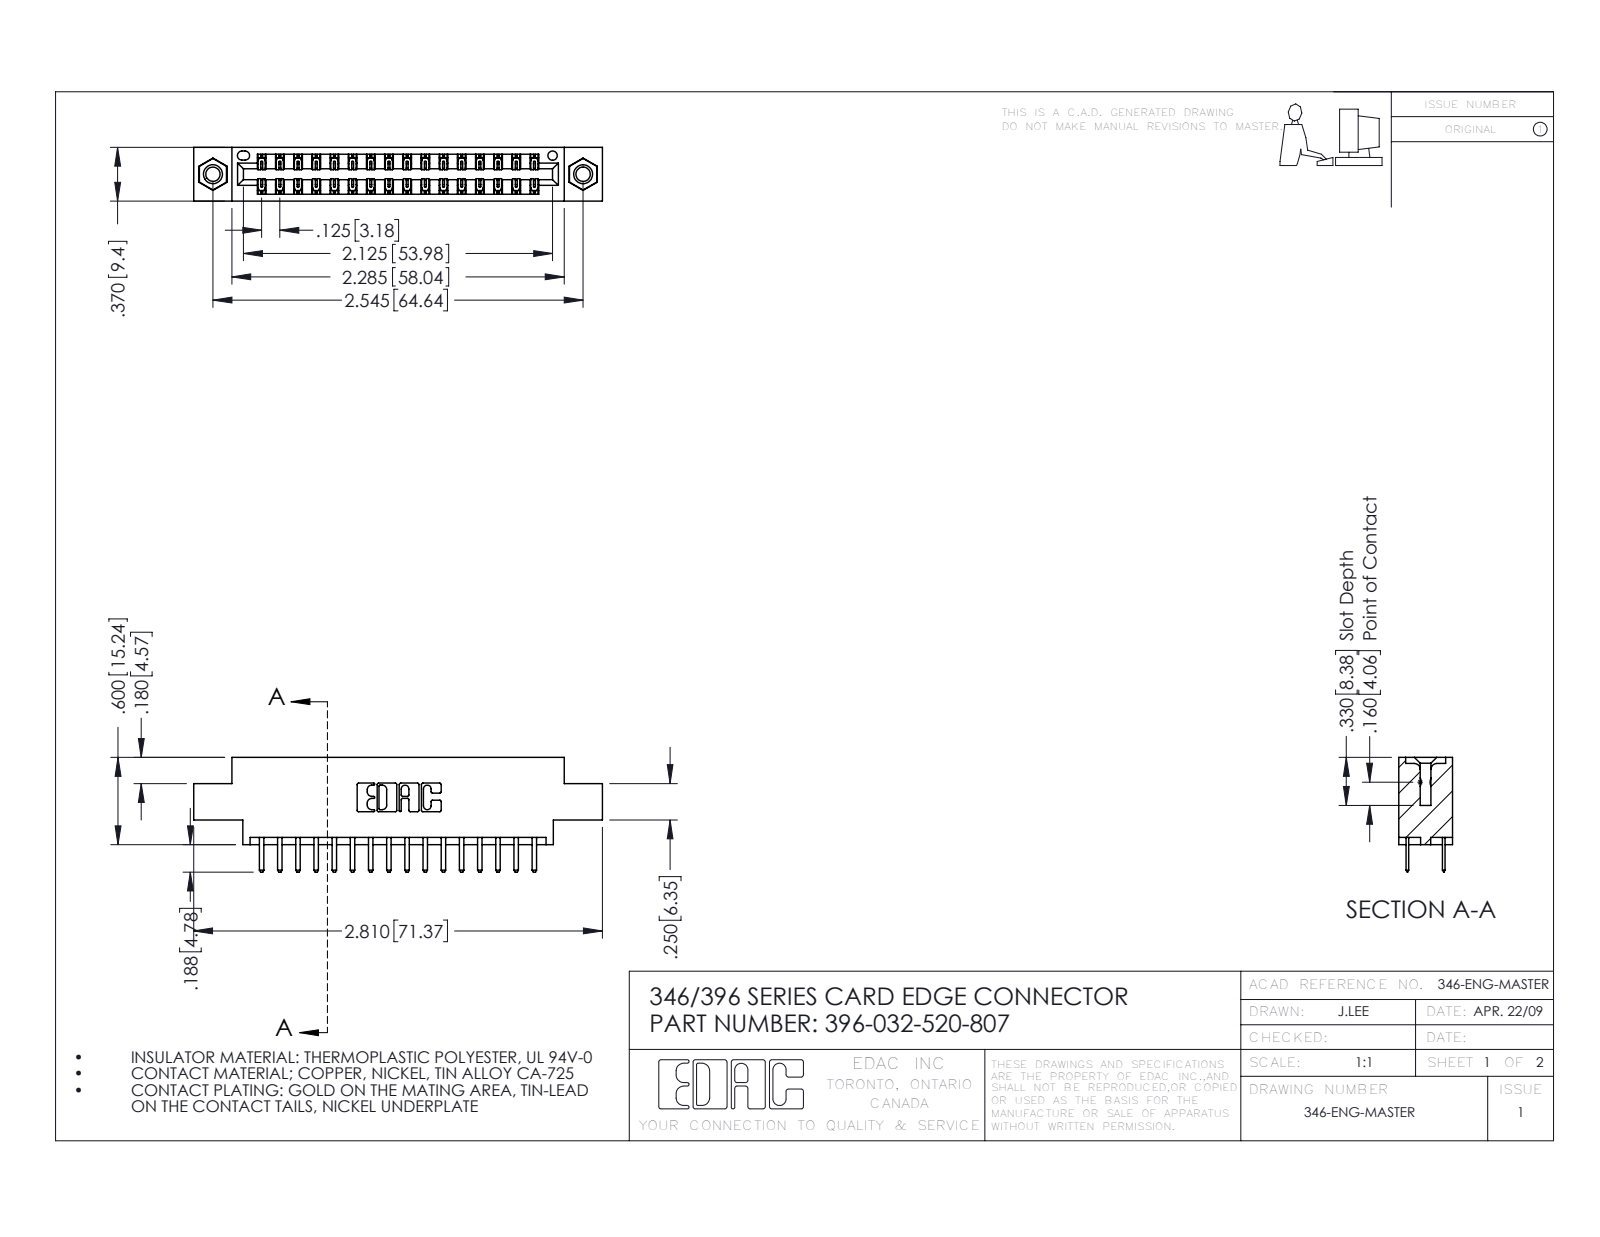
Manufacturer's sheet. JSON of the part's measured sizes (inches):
{"part_name": "345-292-001_345-293-120; 345-250-001_345-250-005-103; 396-032-520-807; 346 Part_0.170 Offset - 0.156 Dia-TI", "step_written_by": "SolidWorks 2016 (CONFIG_CONTROL_DESIGN)", "units": "inches", "bodies": {"solids": 35, "faces": 1978, "planar": 1296, "cylindrical": 666, "other": 16}, "overall_size": [2.81, 0.788, 0.37], "volume_in3": 0.401, "surface_area_in2": 13.66, "round_holes": [[0.098, 2], [0.125, 2], [0.156, 2], [0.064, 1]], "round_bosses_or_shafts": [[0.155, 2]], "partial_cylinders_radius": [[0.006, 48], [0.01, 36], [0.01, 22], [0.007, 6], [0.031, 6], [0.026, 3], [0.014, 2], [0.022, 2]], "face_to_face_distances": [0.25, 0.048, 0.322, 0.37, 0.222, 0.148, 0.275, 0.072, 0.298, 0.025], "hole_center_spacings": [0.246, 2.338, 2.545]}
